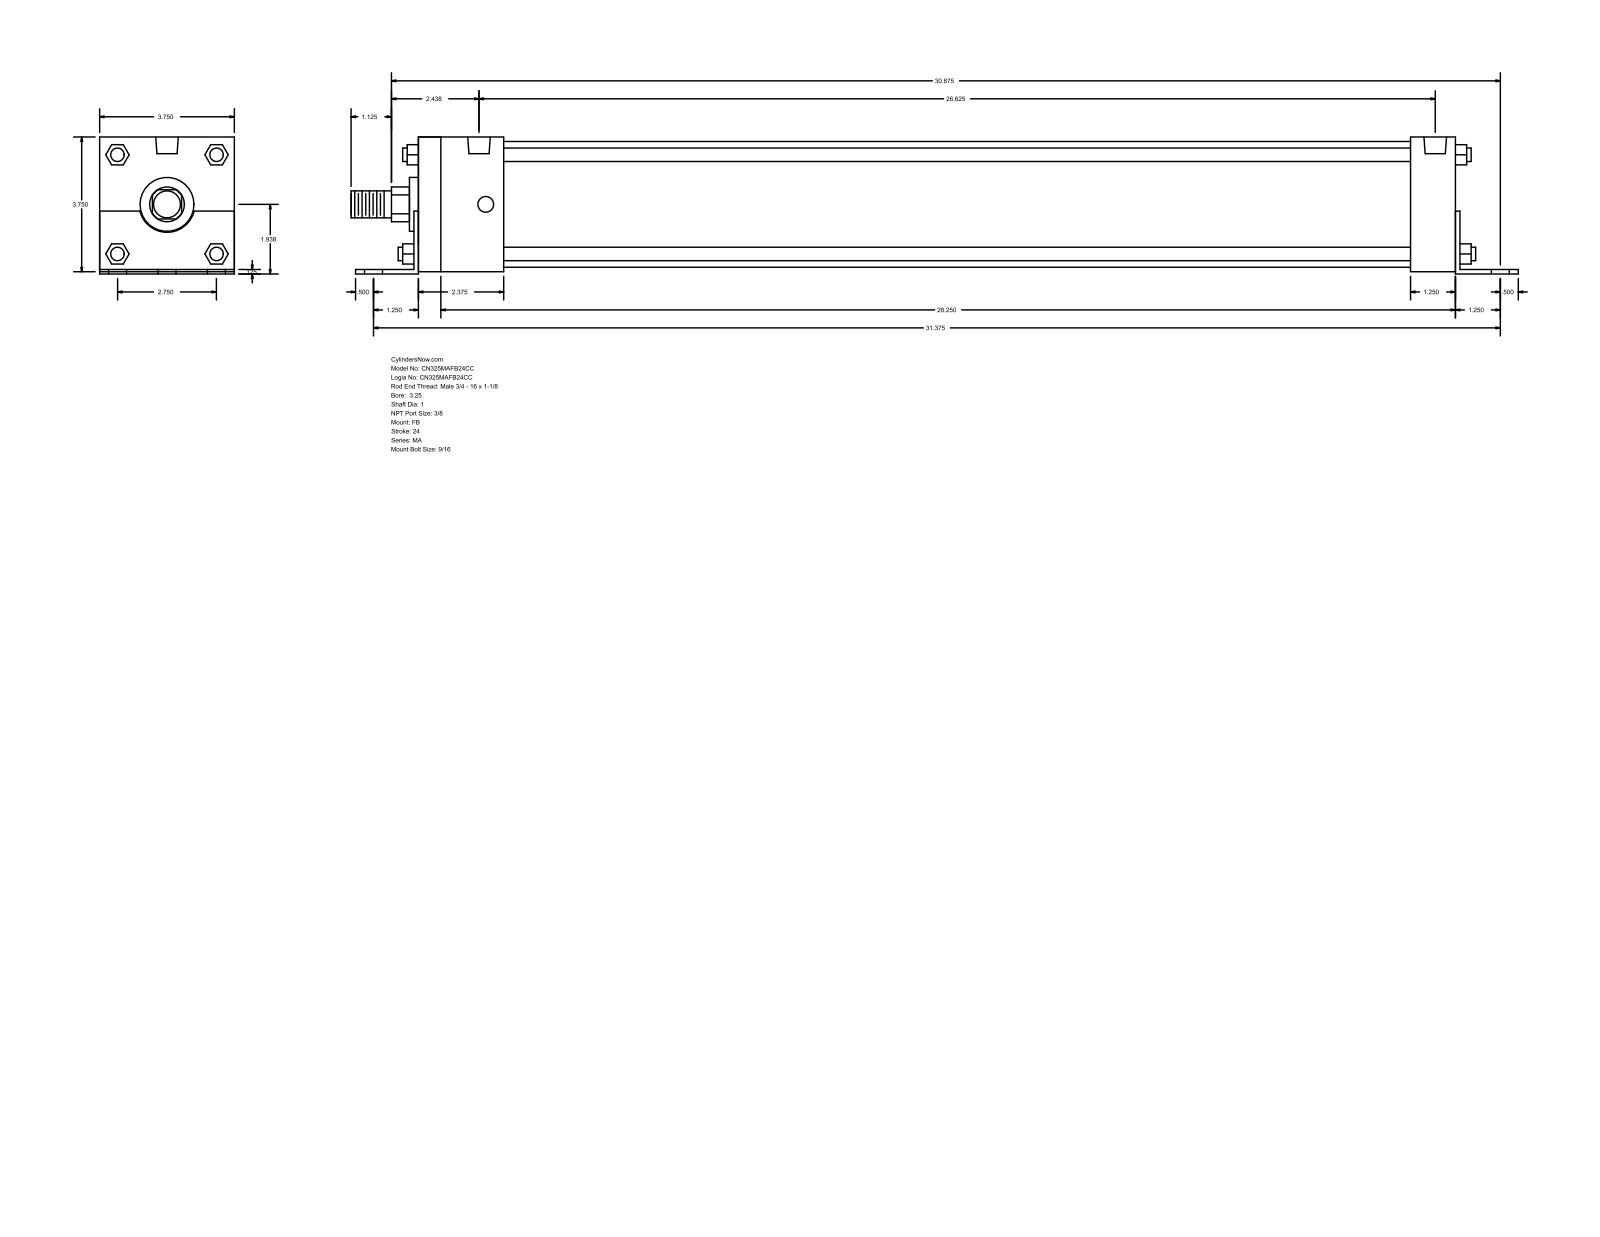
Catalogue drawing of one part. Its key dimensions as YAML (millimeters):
part_name: "MA_FB__0325_1"
step_written_by: "GSSL Pune (CONFIG_CONTROL_DESIGN)"
units: millimeters
bodies: {solids: 0, faces: 140, planar: 105, cylindrical: 35, other: 0}
overall_size: [825.5, 96.84, 95.25]
round_holes:
  - {diameter: 14.29, count: 6}
  - {diameter: 11.11, count: 4}
  - {diameter: 15.93, count: 2}
round_bosses_or_shafts:
  - {diameter: 9.53, count: 4}
  - {diameter: 88.9, count: 1}
  - {diameter: 38.1, count: 1}
  - {diameter: 25.4, count: 1}
  - {diameter: 19.05, count: 1}
partial_cylinders:
  - {radius: 12.29, count: 1}
  - {radius: 19.81, count: 1}
face_to_face_distances: [95.24, 3.17, 1.59, 96.83, 1.58, 93.66, 736.6, 733.43, 739.77, 704.85]
hole_center_spacings: [34.92, 797.69, 796.93, 57.78, 61.65, 69.84, 82.38, 86.71]
